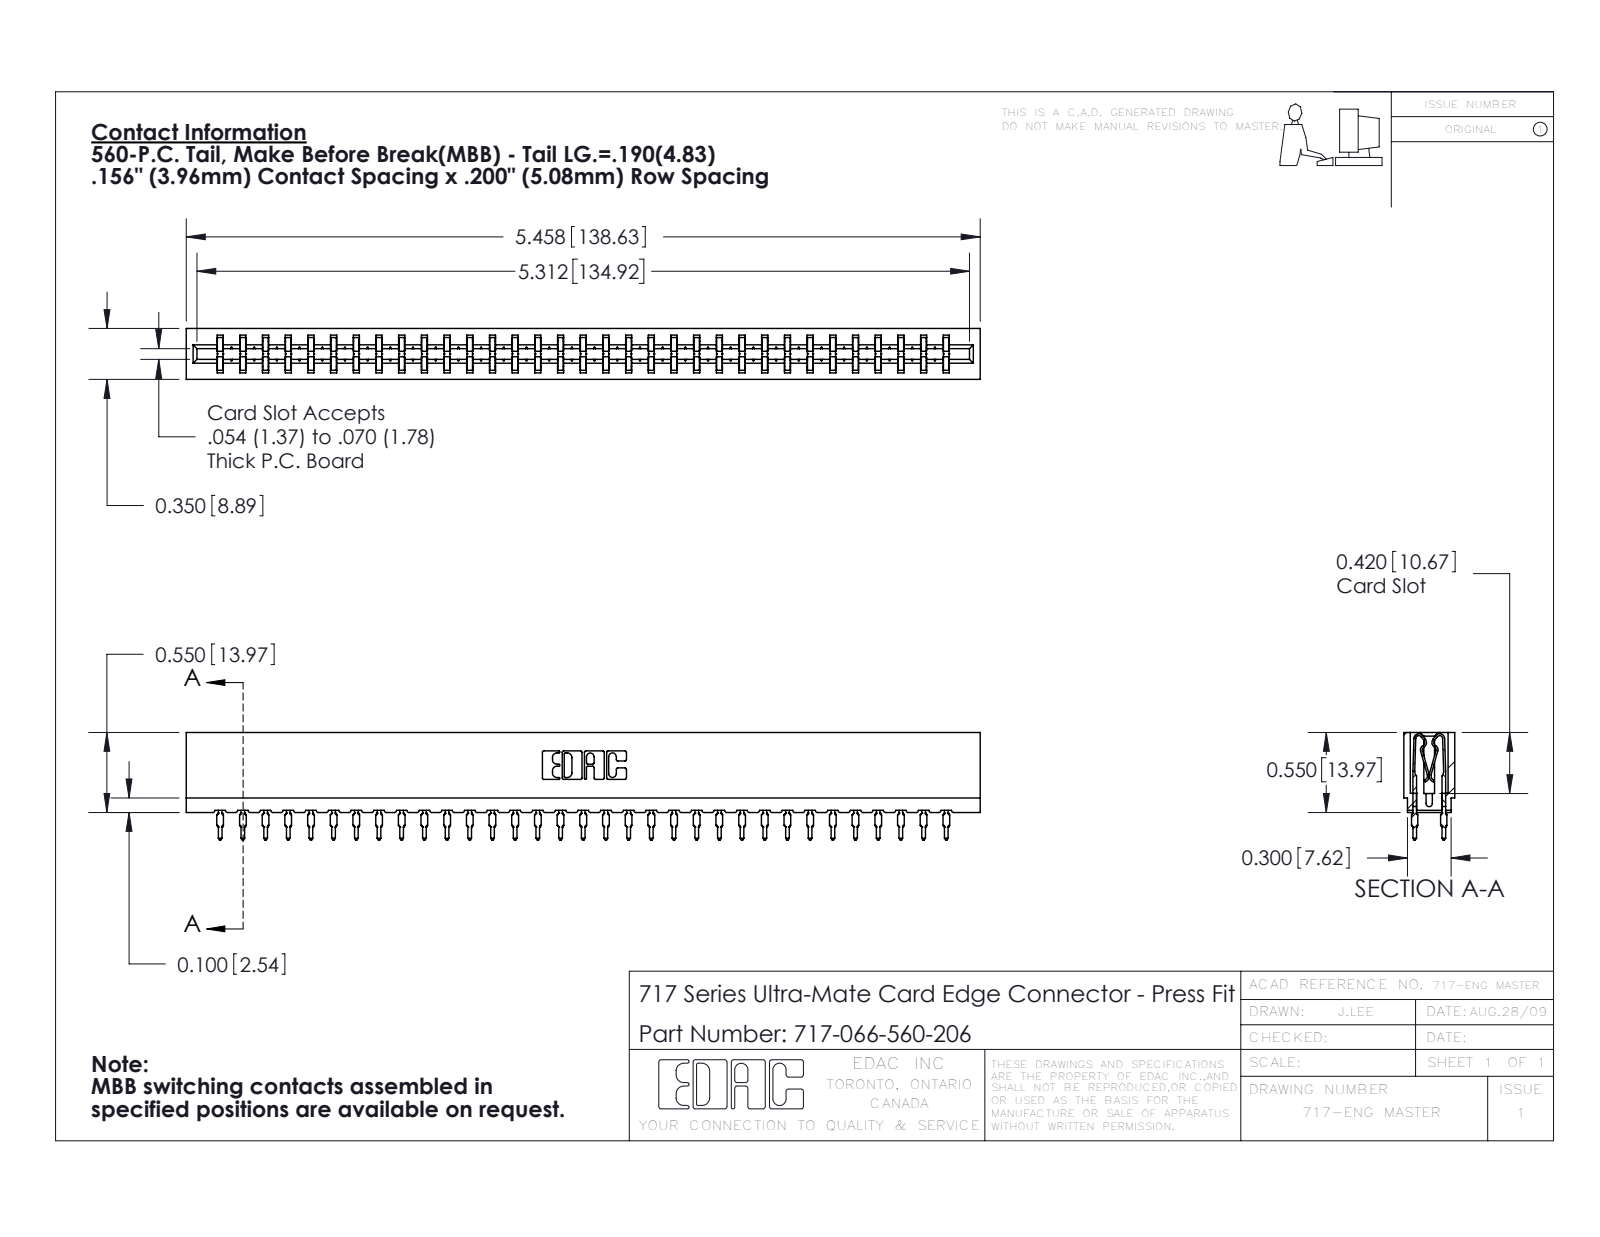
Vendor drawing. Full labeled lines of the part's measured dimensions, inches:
Part name (STEP PRODUCT): 717 Part_Insulator Option - 06; 745-292-001_560; 717-066-560-206
STEP written by: SolidWorks 2016 (CONFIG_CONTROL_DESIGN)
Units: inches
Bodies: 67 solids, 6628 faces (3453 planar, 1459 cylindrical, 1716 other)
Overall size (bounding box): 5.458 × 0.739 × 0.35
Volume: 0.75 in³ · Surface area: 30.76 in²
Partial cylindrical surfaces — rounded edges, fillets, slot ends (radius × count): R0.021 ×132, R0.015 ×66, R0.01 ×22, R0.005 ×8, R0.011 ×8, R0.007 ×6, R0.031 ×6, R0.026 ×3
Main face-to-face distances: 0.212, 0.138, 0.35, 0.063, 0.287, 0.076, 0.149, 0.074, 0.045, 0.305
